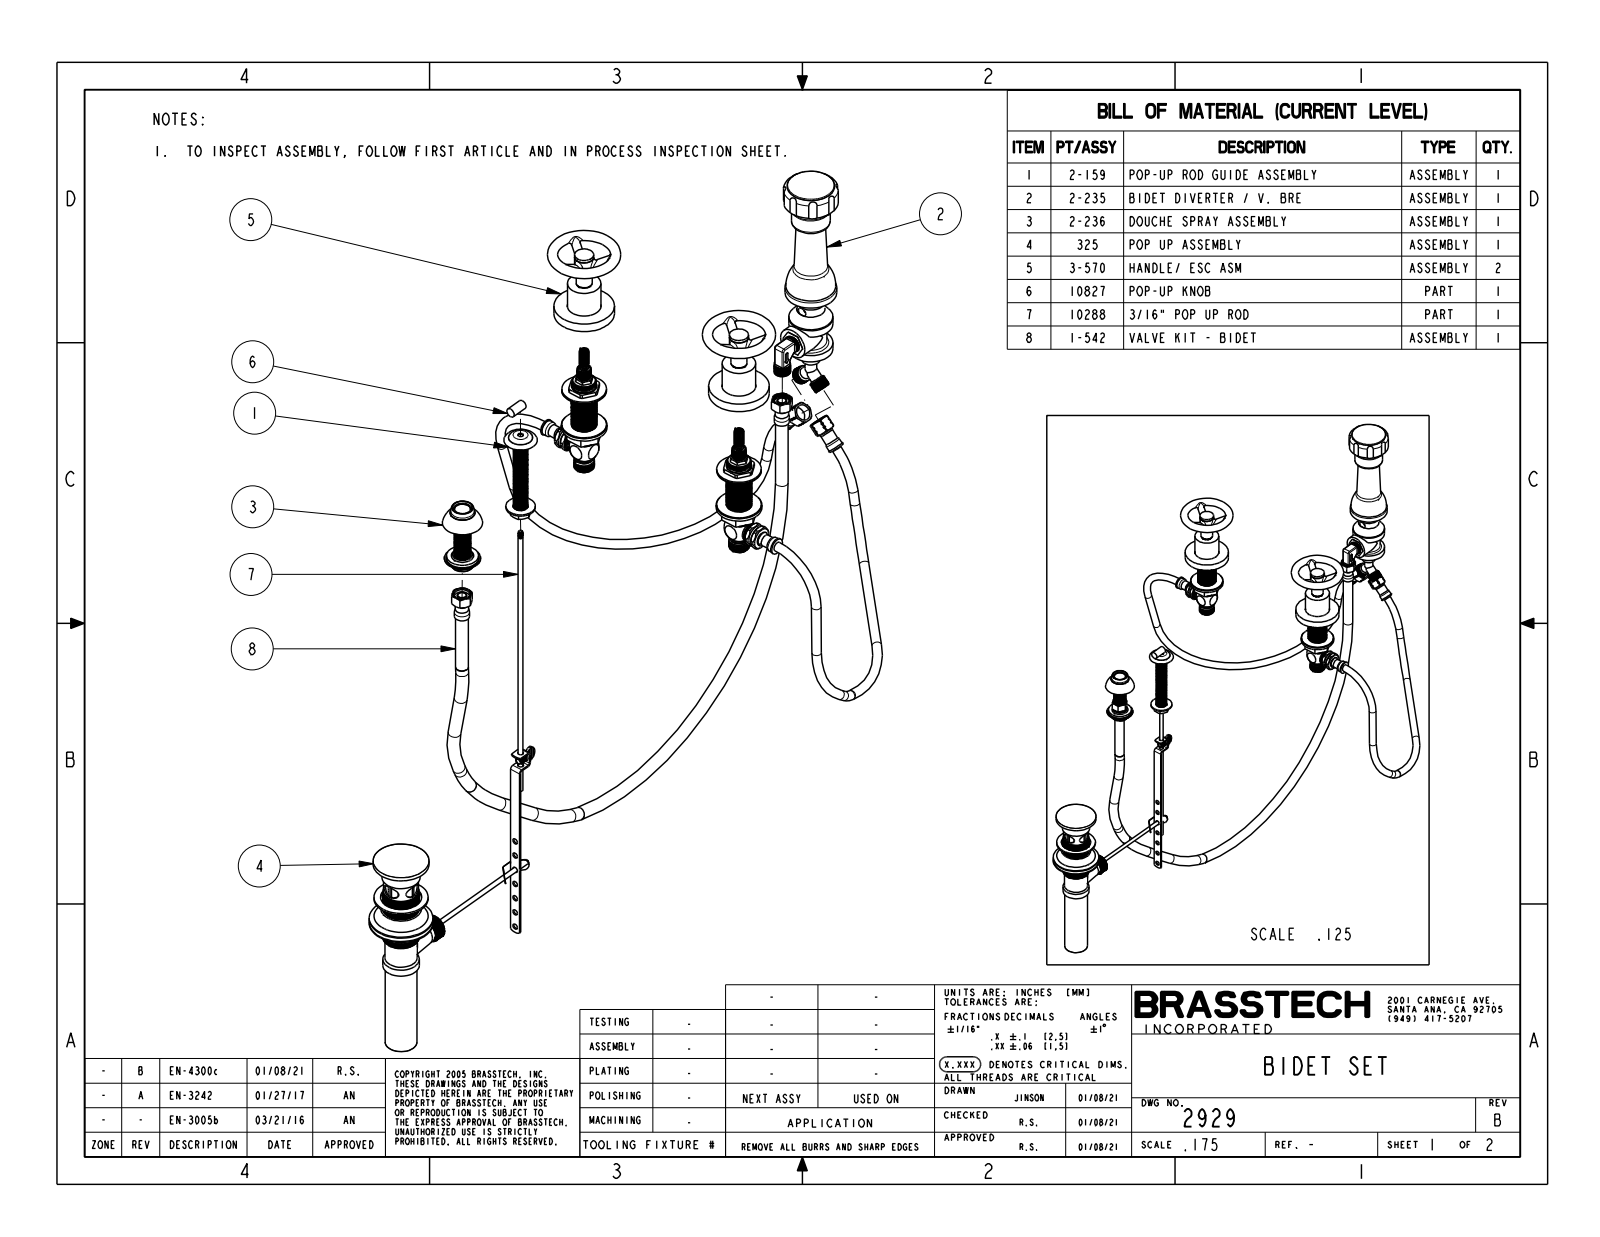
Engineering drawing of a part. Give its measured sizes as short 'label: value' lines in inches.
name: 2929
written by: CREO PARAMETRIC BY PTC INC, 2018400 (CONFIG_CONTROL_DESIGN)
unit: in
bodies: 5 solids, 214 faces (50 planar, 74 cylindrical, 90 other)
size: 22.855 × 10.875 × 5.353
volume: 21.9 in³; area: 111 in²
holes: 1× ⌀0.625, 1× ⌀0.792, 1× ⌀0.94
bosses: 6× ⌀0.35, 2× ⌀2.375, 2× ⌀1.313, 2× ⌀0.75, 2× ⌀0.63, 2× ⌀0.4, 1× ⌀2.025, 1× ⌀1.52
rounds: 8× R0.21, 1× R0.357, 1× R1.077
face distances: 0.375, 1.108, 1.483, 2.893, 2.518, 1.41, 3.468, 3.093, 1.985, 0.575
